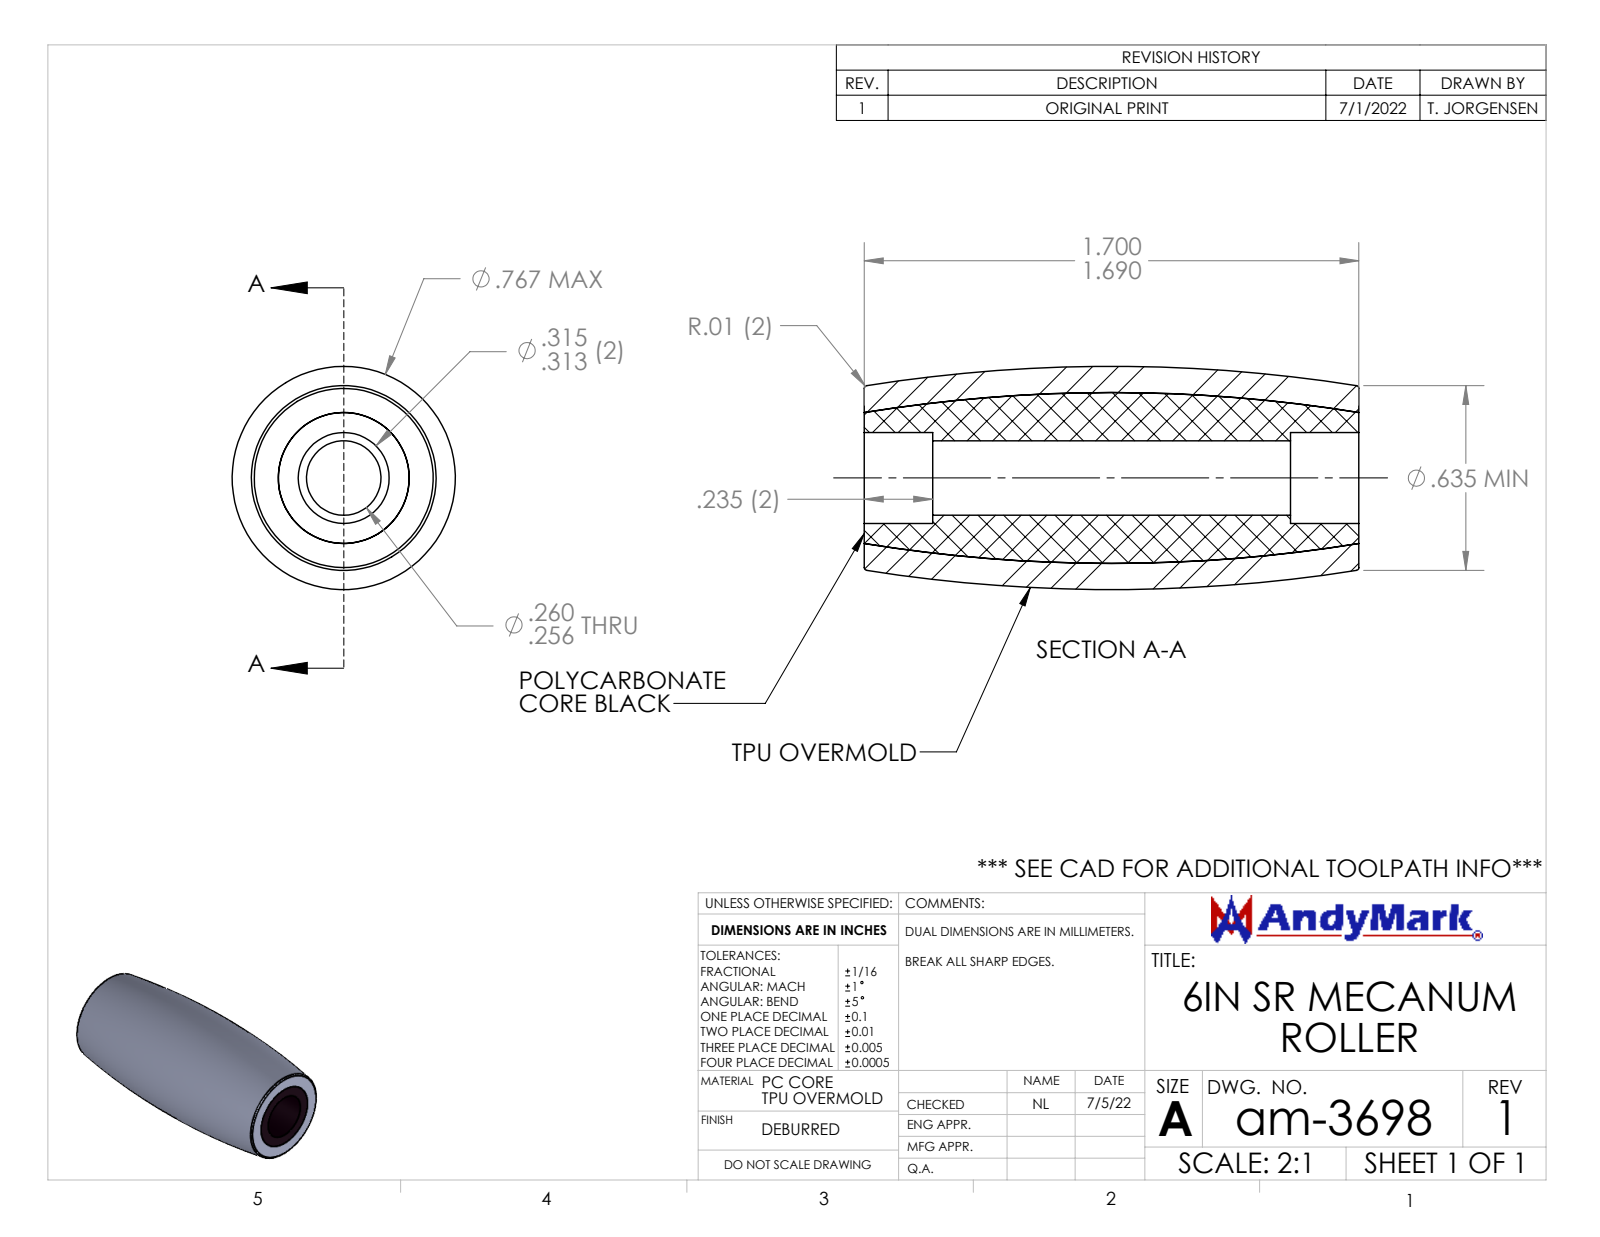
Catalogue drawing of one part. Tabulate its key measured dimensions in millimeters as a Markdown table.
| quantity | value |
| --- | --- |
| part name | am-3698_core PC; am-3698_skin TPU v2; am-3698 6in SR Mecanum Roller |
| STEP written by | SolidWorks 2022 (CONFIG_CONTROL_DESIGN) |
| units | millimeters |
| bodies | 2 solids, 22 faces (6 planar, 6 cylindrical, 10 other) |
| overall size | 43.2 × 19.5 × 19.5 |
| volume | 9 820 mm³ |
| surface area | 7 510 mm² |
| round holes (diameter × count) | 6.5 × 1, 8 × 1 |
| main face-to-face distances | 43.2, 37.2, 6, 6, 31.2, 37.2 |
